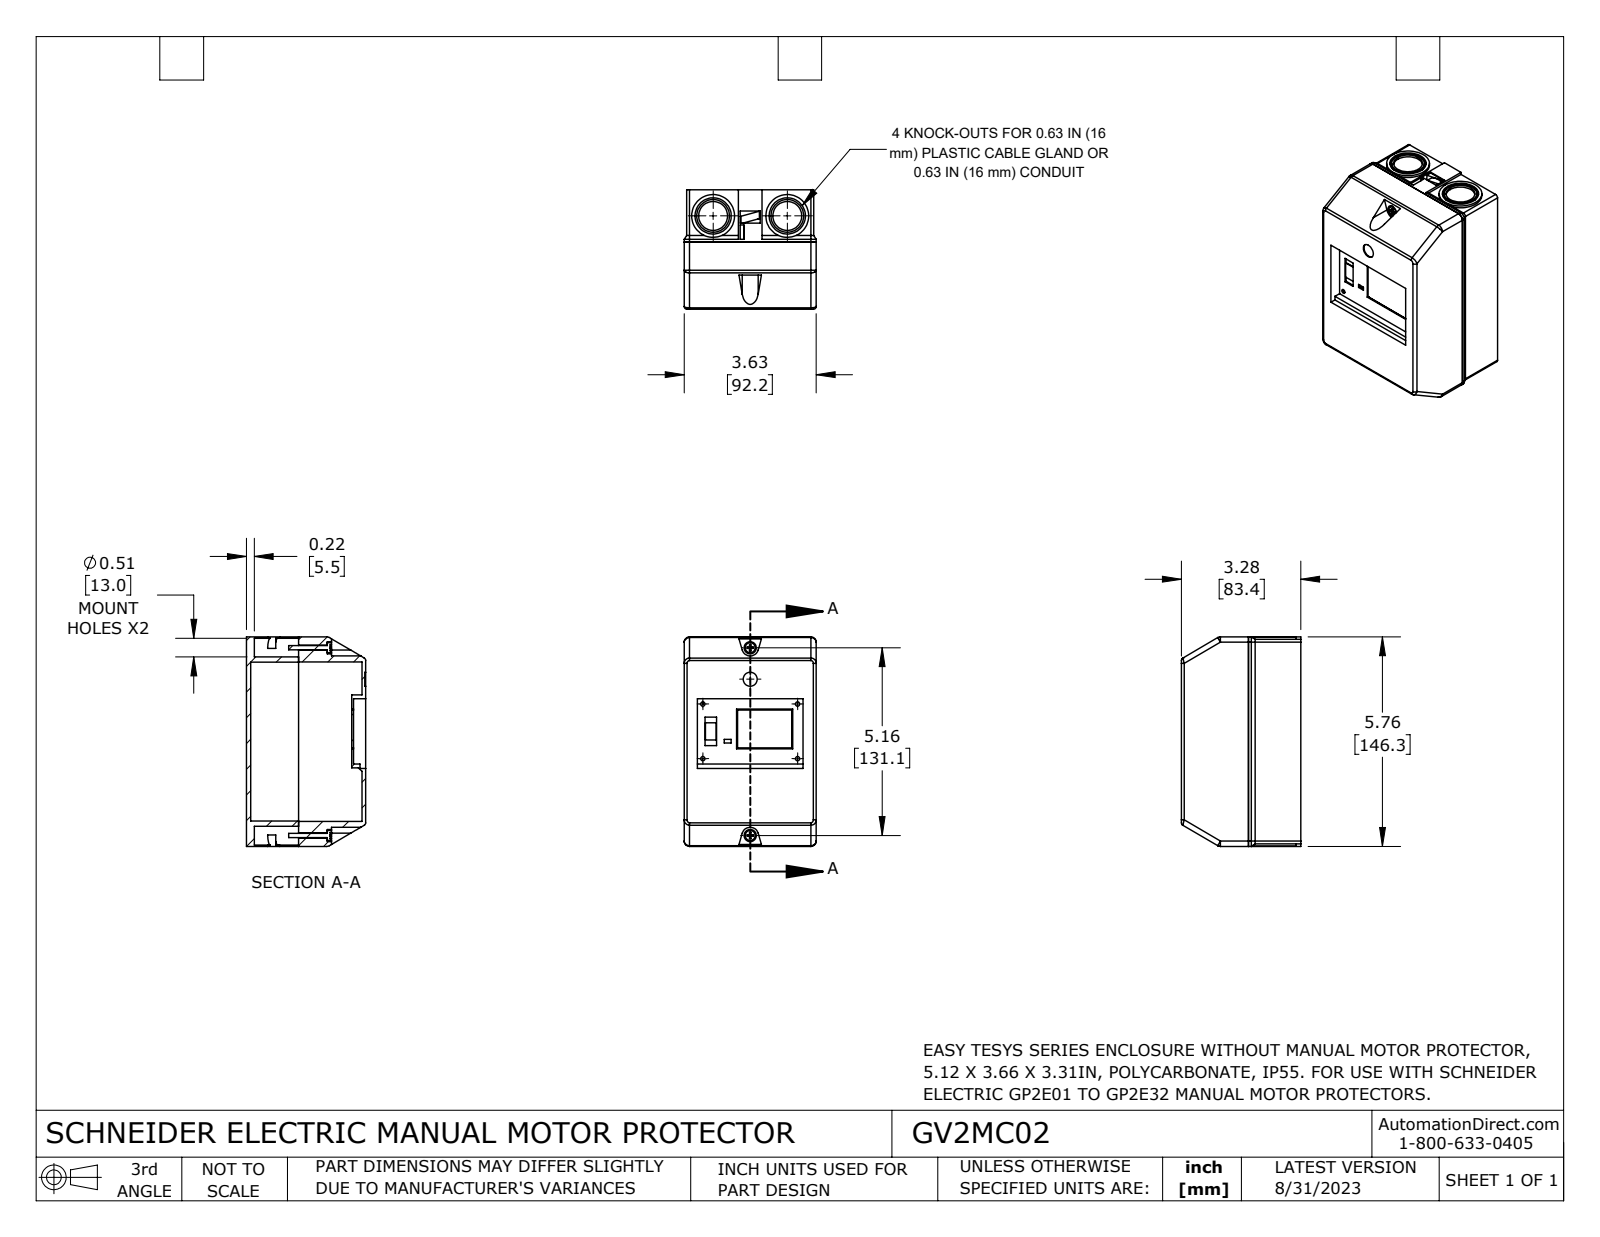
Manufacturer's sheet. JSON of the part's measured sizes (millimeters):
{"part_name": "GV2MC02", "step_written_by": "SolidWorks 2021 (CONFIG_CONTROL_DESIGN)", "units": "millimeters", "bodies": {"solids": 4, "faces": 283, "planar": 173, "cylindrical": 94, "other": 16}, "overall_size": [146.3, 92.2, 83.3], "volume_mm3": 246800, "surface_area_mm2": 132100, "round_holes": [[3, 4], [3.5, 2], [8.5, 2], [13, 2], [20.1, 2], [25.3, 2], [9.8, 1]], "round_bosses_or_shafts": [[29.9, 2], [22.9, 2], [6.9, 2], [2.9, 2]], "partial_cylinders_radius": [[3.8, 10], [2, 8], [5.7, 2], [10.2, 2]], "face_to_face_distances": [2.6, 3.7, 1.8, 2, 3, 88.5, 89.6, 1.1, 85.9, 90.4], "hole_center_spacings": [37.4, 38.2, 51.4, 51.5, 63, 63.1, 64.6, 66.2]}
